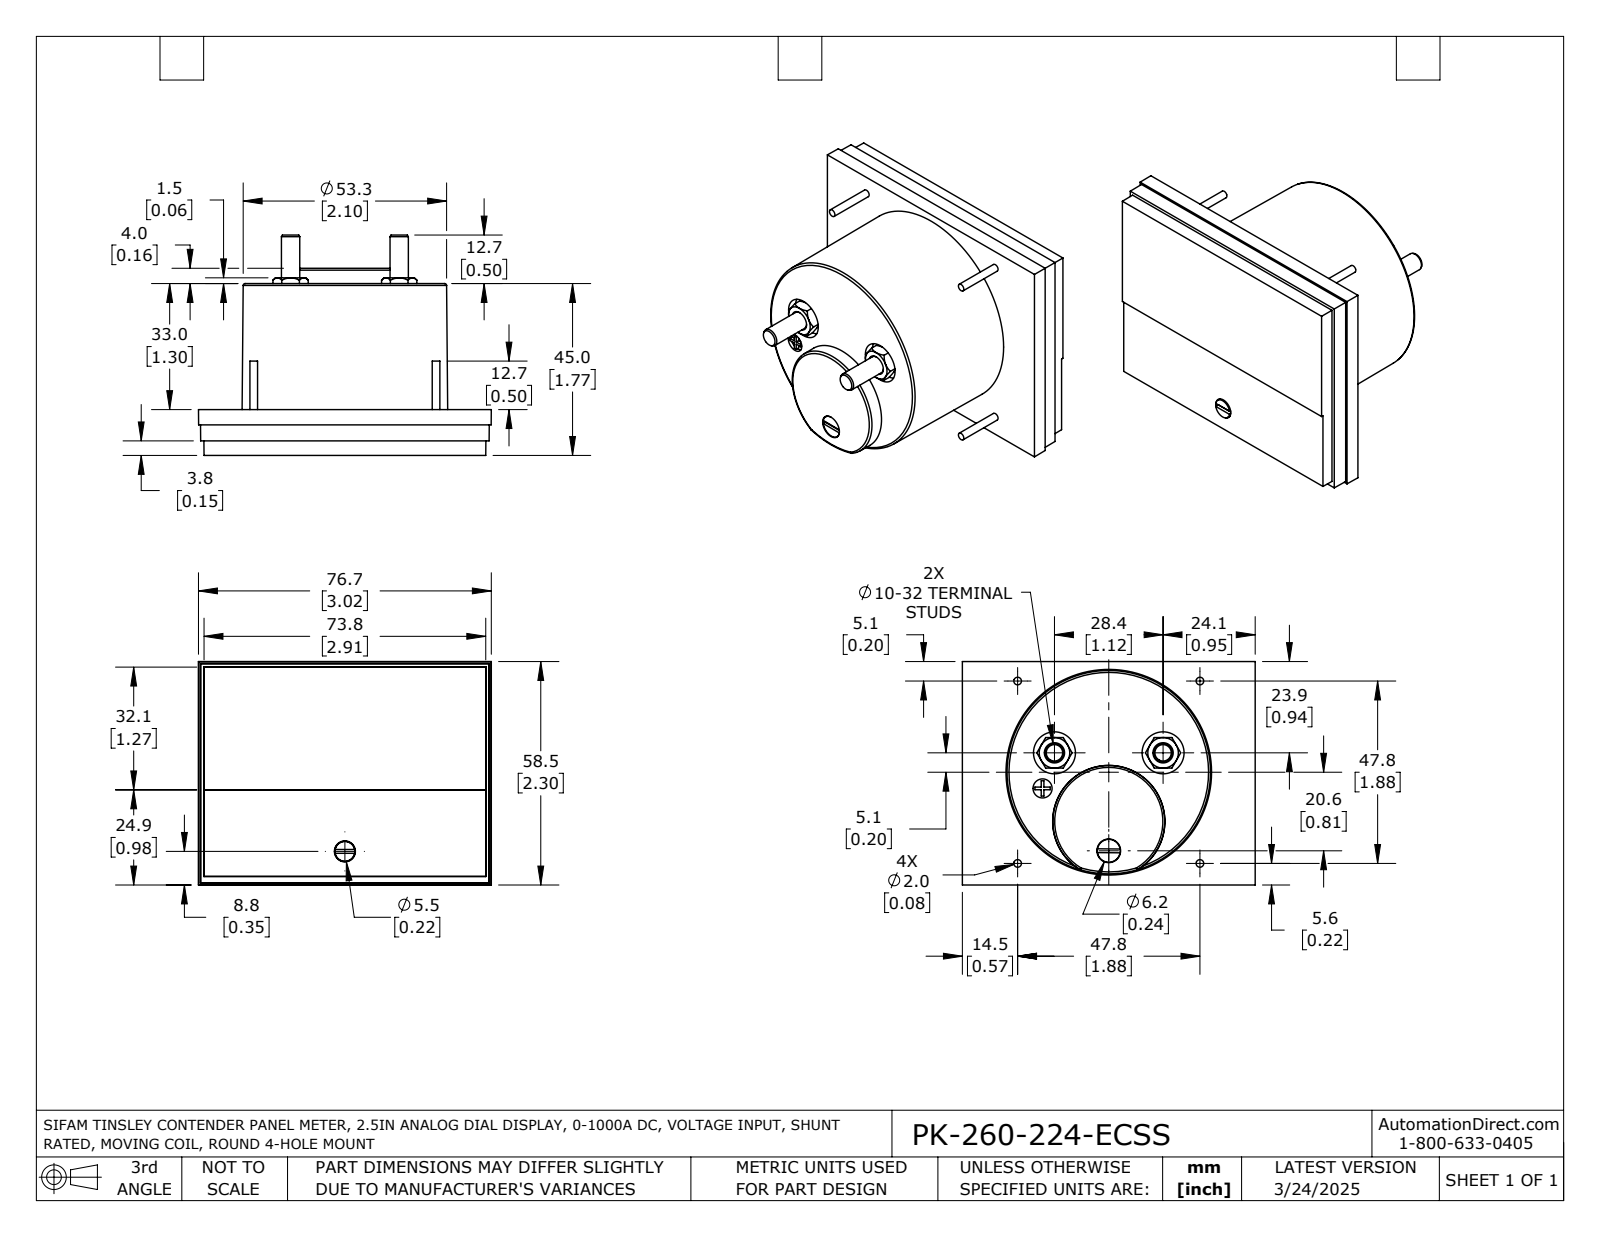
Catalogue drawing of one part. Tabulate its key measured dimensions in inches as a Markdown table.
| quantity | value |
| --- | --- |
| part name | PK-260-224-ECSS |
| STEP written by | SolidWorks 2021 (AUTOMOTIVE_DESIGN) |
| units | inches |
| bodies | 1 solid, 192 faces (95 planar, 37 cylindrical, 60 other) |
| overall size | 3.02 × 2.303 × 2.272 |
| volume | 7.657 in³ |
| surface area | 36.55 in² |
| round holes (diameter × count) | 0.197 × 3, 0.433 × 2, 0.209 × 1, 0.217 × 1, 0.244 × 1 |
| round bosses / shafts (diameter × count) | 0.079 × 4, 0.189 × 2, 0.236 × 1, 0.205 × 1 |
| partial cylindrical surfaces (radius × count) | 0.033 × 1 |
| main face-to-face distances | 0.02, 0.472, 0.13, 0.322, 0.15, 0.453, 0.057, 0.077, 0.396, 0.073 |
| hole center spacings | 1.155, 1.16, 0.387, 0.938, 0.942, 1.12, 1.295 |
